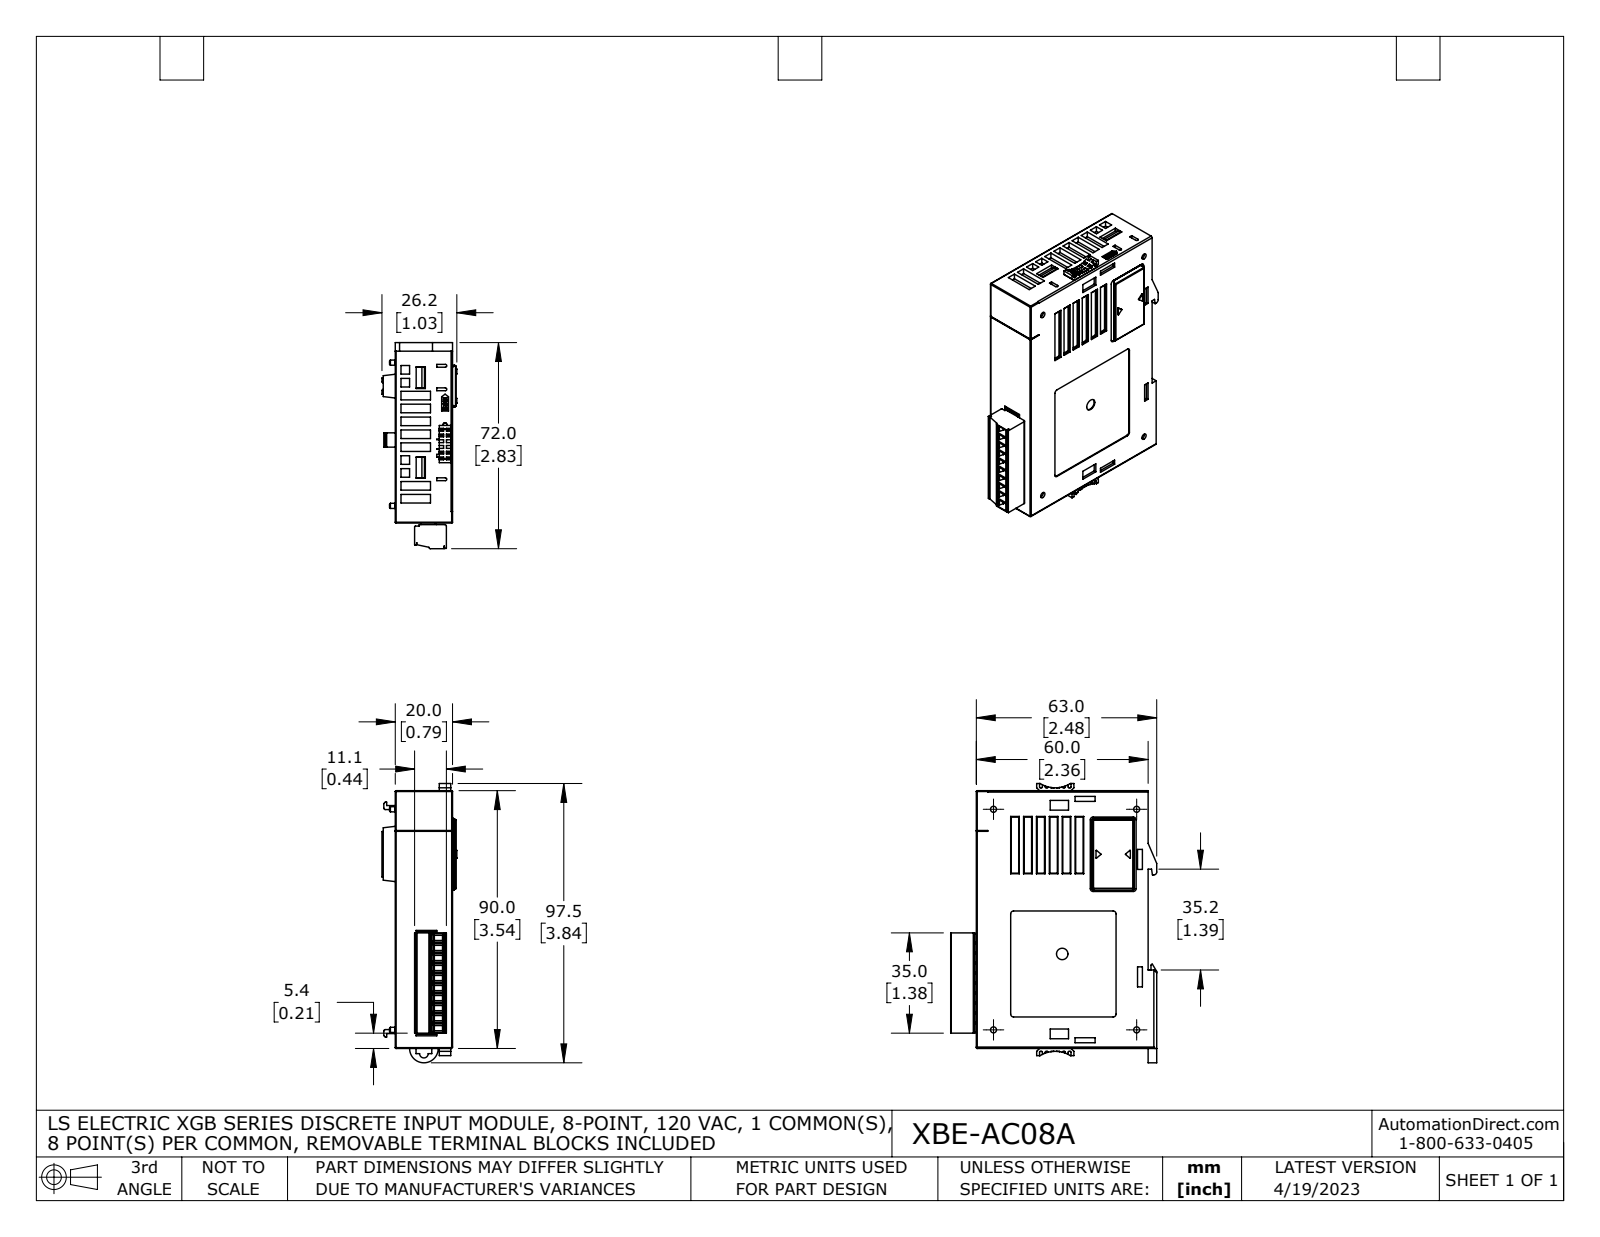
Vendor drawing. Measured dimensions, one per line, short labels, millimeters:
name: XBE-AC08A nc coord fxt
written by: SolidWorks 2021 (AUTOMOTIVE_DESIGN)
unit: mm
bodies: 1 solid, 2617 faces (1995 planar, 449 cylindrical, 173 other)
size: 97.5 × 72 × 26.2
volume: 109 600 mm³; area: 27 750 mm²
holes: 10× ⌀1.2, 10× ⌀2.7, 10× ⌀2.9, 4× ⌀2.1, 1× ⌀4
bosses: 10× ⌀2.8, 4× ⌀1.8, 2× ⌀2
rounds: 70× R0.1, 60× R0.3, 46× R0.2, 25× R0.5, 11× R1, 10× R1.6, 10× R1.8, 6× R0.8
face distances: 20, 19.7, 60, 0.8, 1, 1.5, 2, 18.7, 19, 90
hole spacings: 3.5, 7, 10.5, 14, 17.5, 21, 24.5, 28
